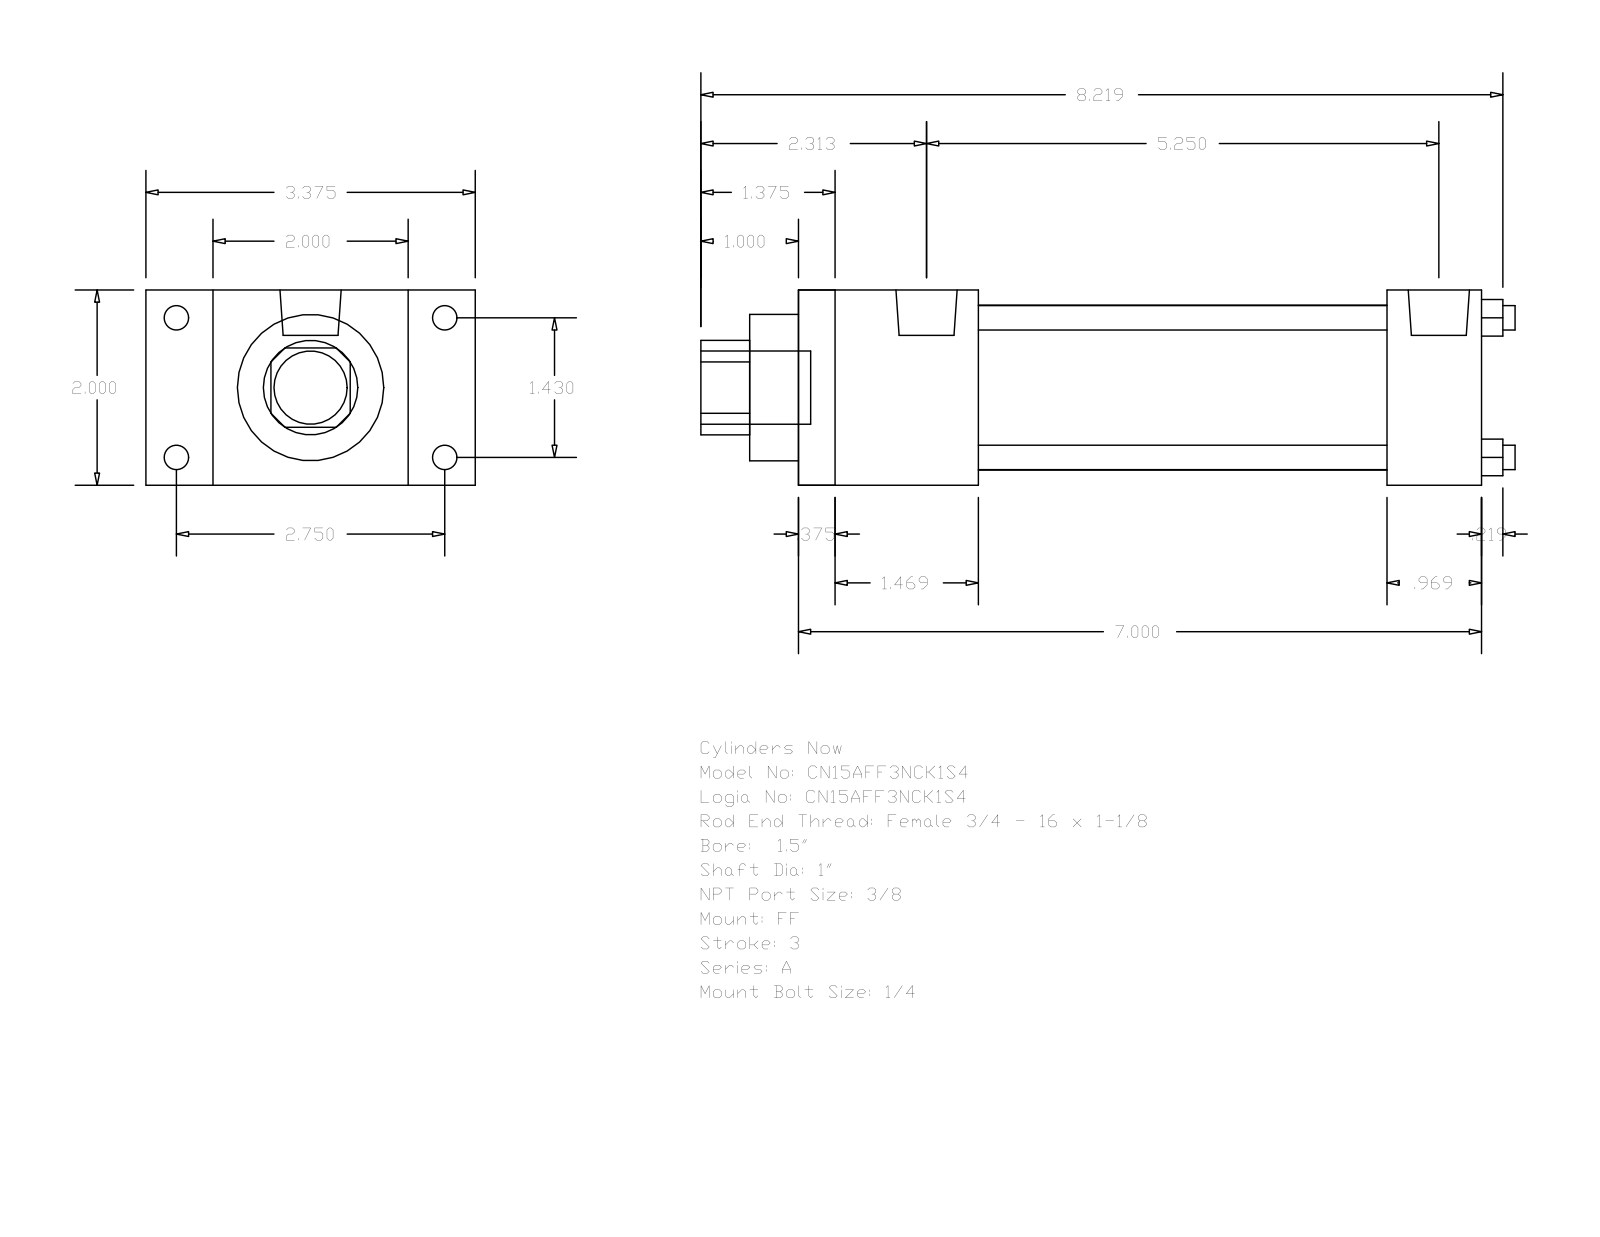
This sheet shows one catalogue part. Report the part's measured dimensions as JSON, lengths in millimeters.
{"part_name": "A_FF__0150_1", "step_written_by": "GSSL Pune (CONFIG_CONTROL_DESIGN)", "units": "millimeters", "bodies": {"solids": 0, "faces": 92, "planar": 64, "cylindrical": 28, "other": 0}, "overall_size": [211.93, 85.72, 50.8], "round_holes": [[6.35, 4], [25.4, 1], [38.1, 1], [42.93, 1]], "round_bosses_or_shafts": [[6.35, 4], [5.56, 4], [15.93, 2], [19.05, 1]], "partial_cylinders_radius": [[12.29, 1]], "face_to_face_distances": [50.8, 177.8, 9.52, 168.28, 46.83, 153.19, 37.31, 143.67, 106.36, 130.97], "hole_center_spacings": [25.68, 36.32, 51.36]}
